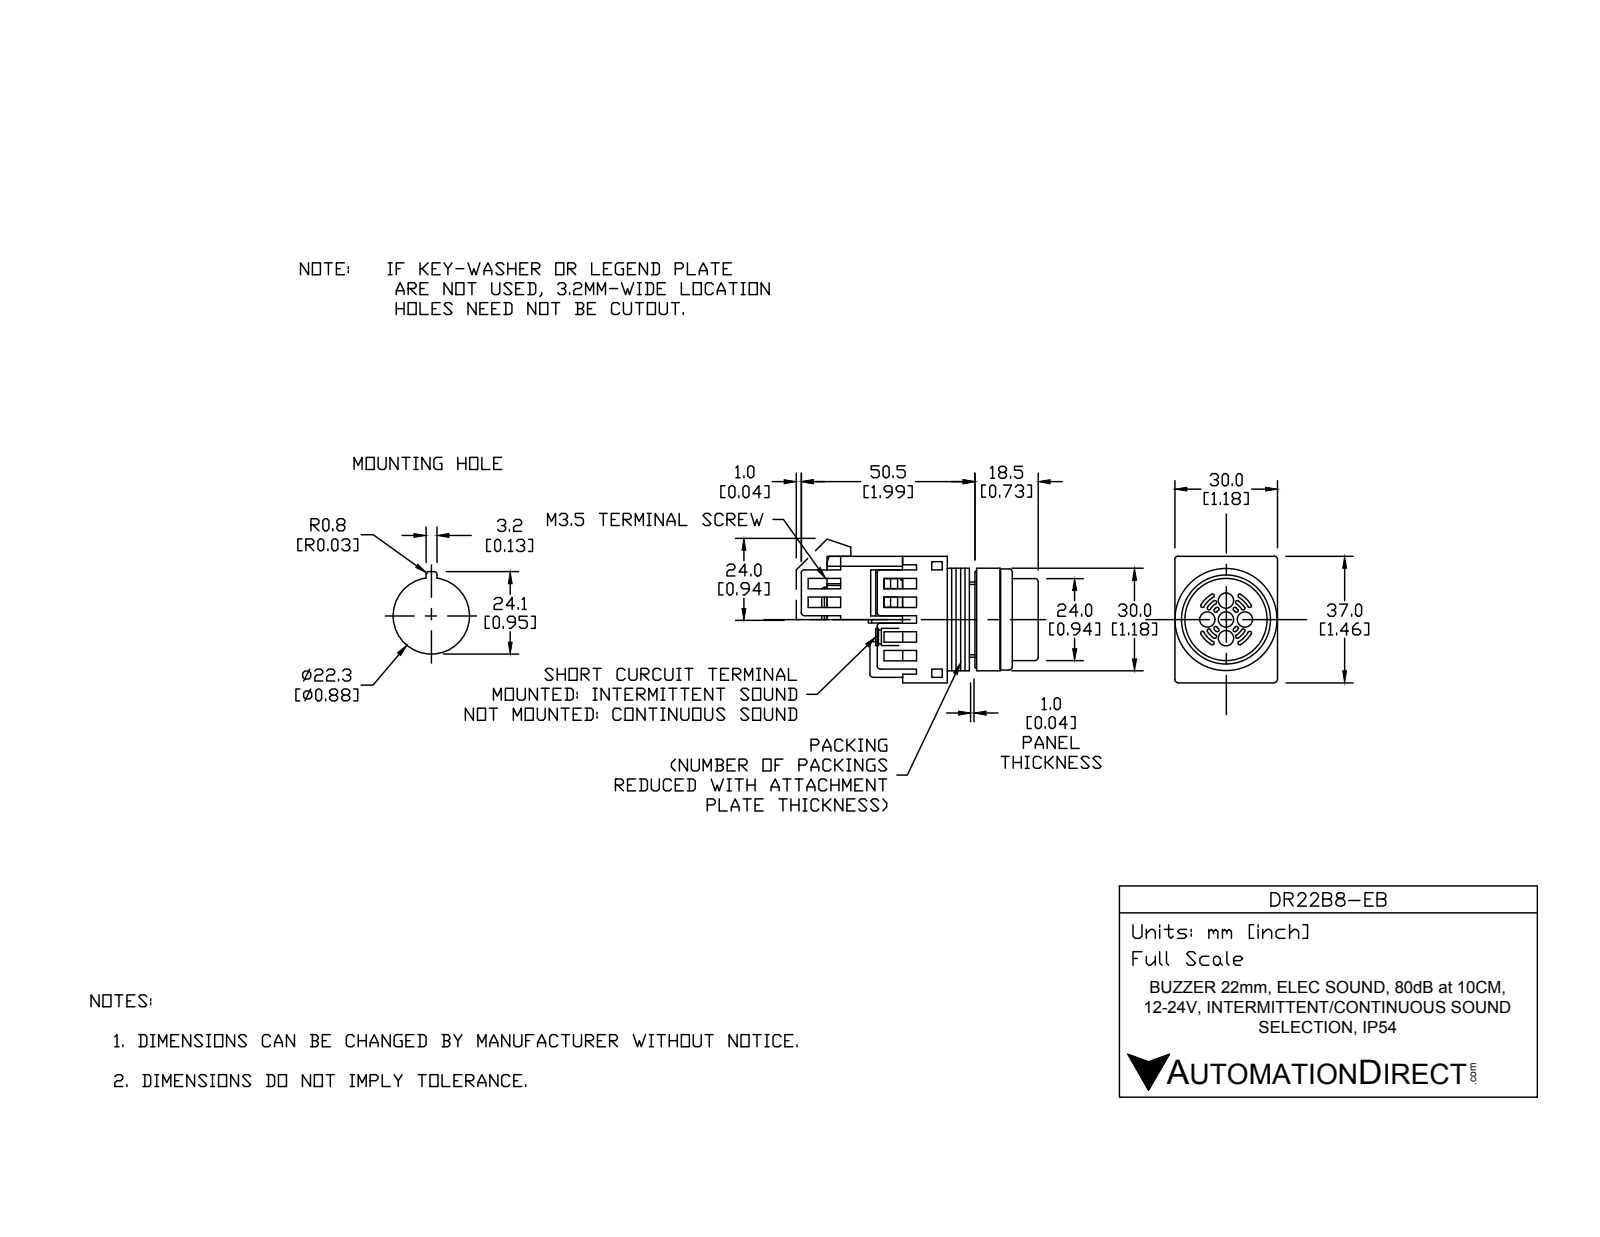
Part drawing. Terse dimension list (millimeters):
name: DR22B8-EB
written by: SolidWorks 2017 (AUTOMOTIVE_DESIGN)
unit: mm
bodies: 13 solids, 196 faces (113 planar, 71 cylindrical, 12 other)
size: 63.5 × 42 × 30.8
volume: 39 666 mm³; area: 19 942 mm²
holes: 3× ⌀2.2, 2× ⌀7, 1× ⌀2.5, 1× ⌀4, 1× ⌀20.8, 1× ⌀22.5
bosses: 2× ⌀5, 1× ⌀30.8, 1× ⌀29.5, 1× ⌀22, 1× ⌀20.2
rounds: 10× R0.5, 2× R2, 2× R4.5
face distances: 1.5, 3, 1.25, 4.5, 2.75, 1.75, 30, 18.5, 13, 4.25
hole spacings: 4.5, 6.36, 7.11, 15.69, 18.34, 19.7, 21.91, 24.82
